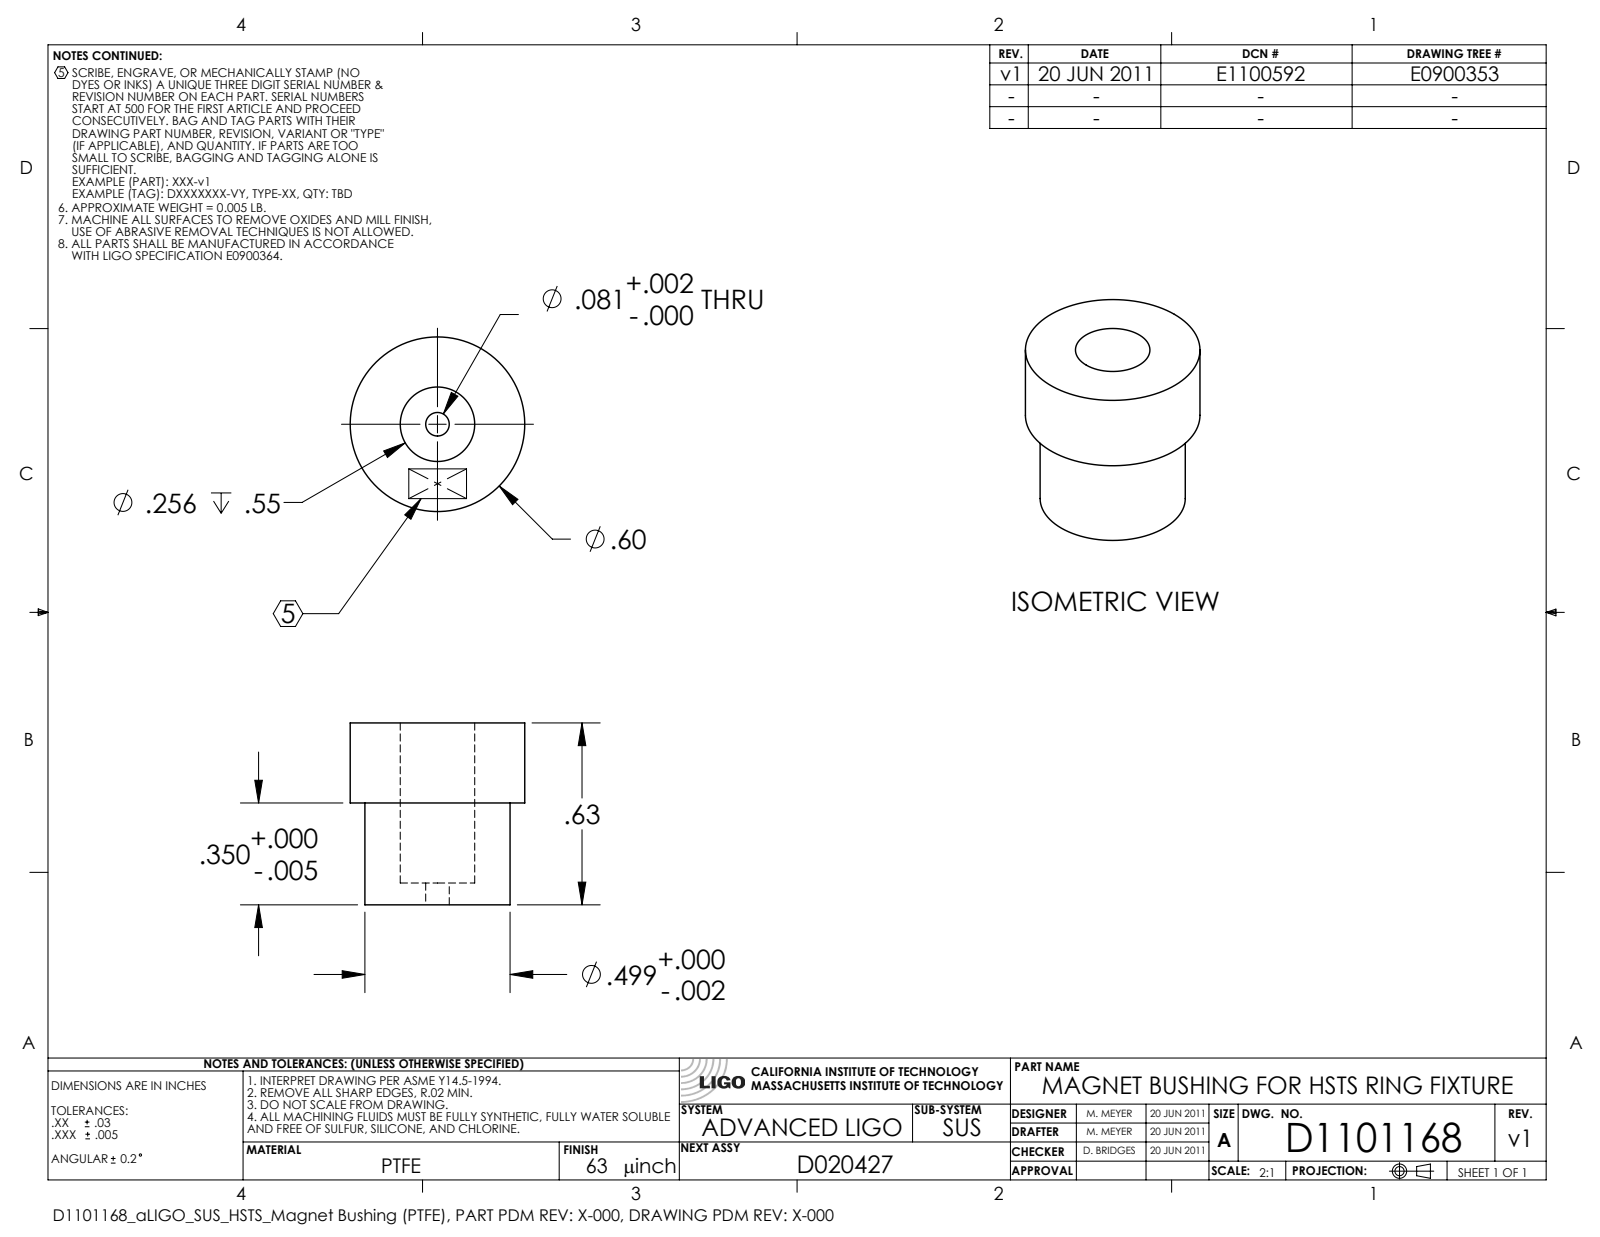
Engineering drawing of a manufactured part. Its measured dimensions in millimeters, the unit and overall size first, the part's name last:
Units: millimetres
Overall size (bounding box): 15.9 × 15.2 × 15.2
Round holes (diameter × count): ⌀2.1 ×1, ⌀6.5 ×1
Round bosses / shafts (diameter × count): ⌀15.2 ×1, ⌀12.7 ×1
Main face-to-face distances: 15.9, 7, 8.9, 1.9, 14
Volume: 1 930 mm³ · Surface area: 1 345 mm²
Bodies: 1 solid, 12 faces (4 planar, 8 cylindrical, 0 other)
Part name (STEP PRODUCT): D1101168-v1_aLIGO_SUS_HSTS_Magnet Bushing (PTFE)
STEP written by: SolidWorks 2010 (CONFIG_CONTROL_DESIGN)
